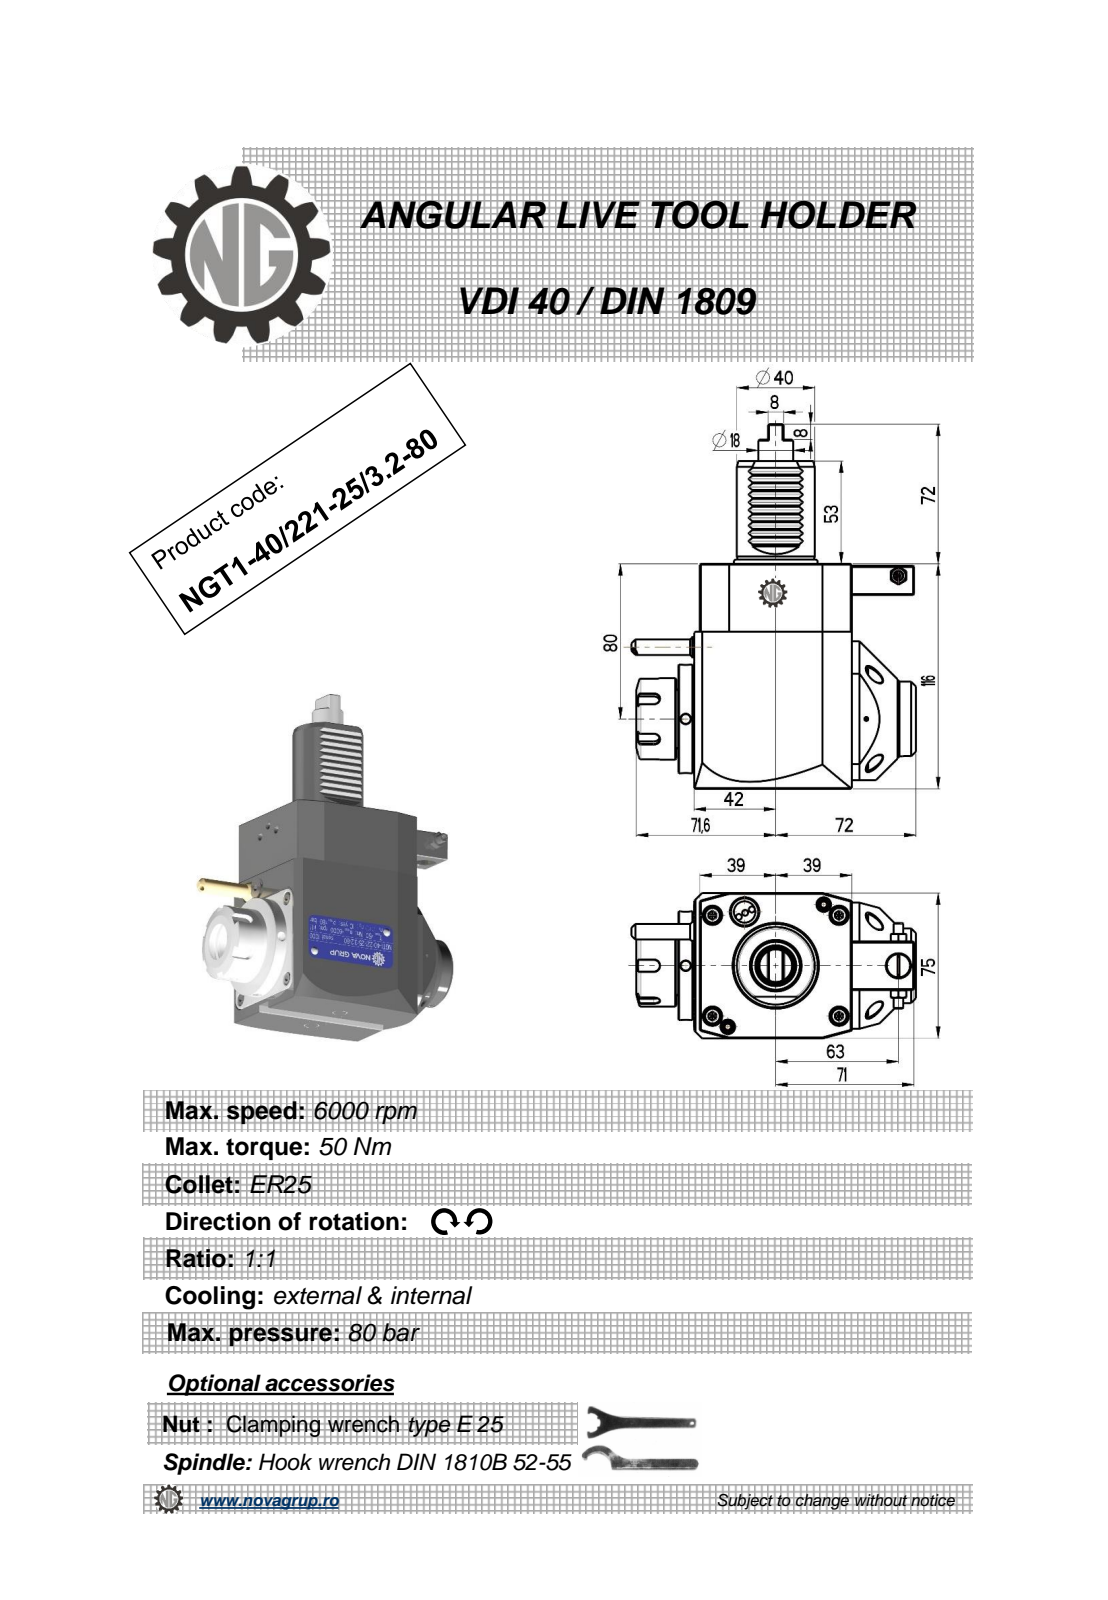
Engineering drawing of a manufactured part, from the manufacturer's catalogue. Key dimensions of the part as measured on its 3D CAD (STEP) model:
Part name (STEP PRODUCT): NGT1_40_221_25_3_2_80
STEP written by: PRO/ENGINEER BY PARAMETRIC TECHNOLOGY CORPORATION, 2010280 (CONFIG_CONTROL_DESIGN)
Units: millimetres
Bodies: 1 solid, 434 faces (194 planar, 91 cylindrical, 149 other)
Overall size (bounding box): 188 × 146.14 × 75
Volume: 886 673 mm³ · Surface area: 71 732 mm²
Round holes (diameter × count): ⌀5 ×3, ⌀3 ×1, ⌀4.2 ×1, ⌀4.5 ×1, ⌀9.5 ×1, ⌀12 ×1, ⌀20.3 ×1
Round bosses / shafts (diameter × count): ⌀56 ×1, ⌀43 ×1, ⌀42 ×1, ⌀40 ×1, ⌀38.5 ×1, ⌀33 ×1, ⌀17.8 ×1, ⌀11.2 ×1
Partial cylindrical surfaces — rounded edges, fillets, slot ends (radius × count): R0.26 ×12, R0.3 ×10, R0.22 ×6, R3 ×5, R0.8 ×2, R0.5 ×1, R40 ×1
Main face-to-face distances: 75, 116, 81, 78, 3, 8, 11, 2.8, 80.8, 8.2
Hole centre spacings: 39.54, 40.93, 72.45
